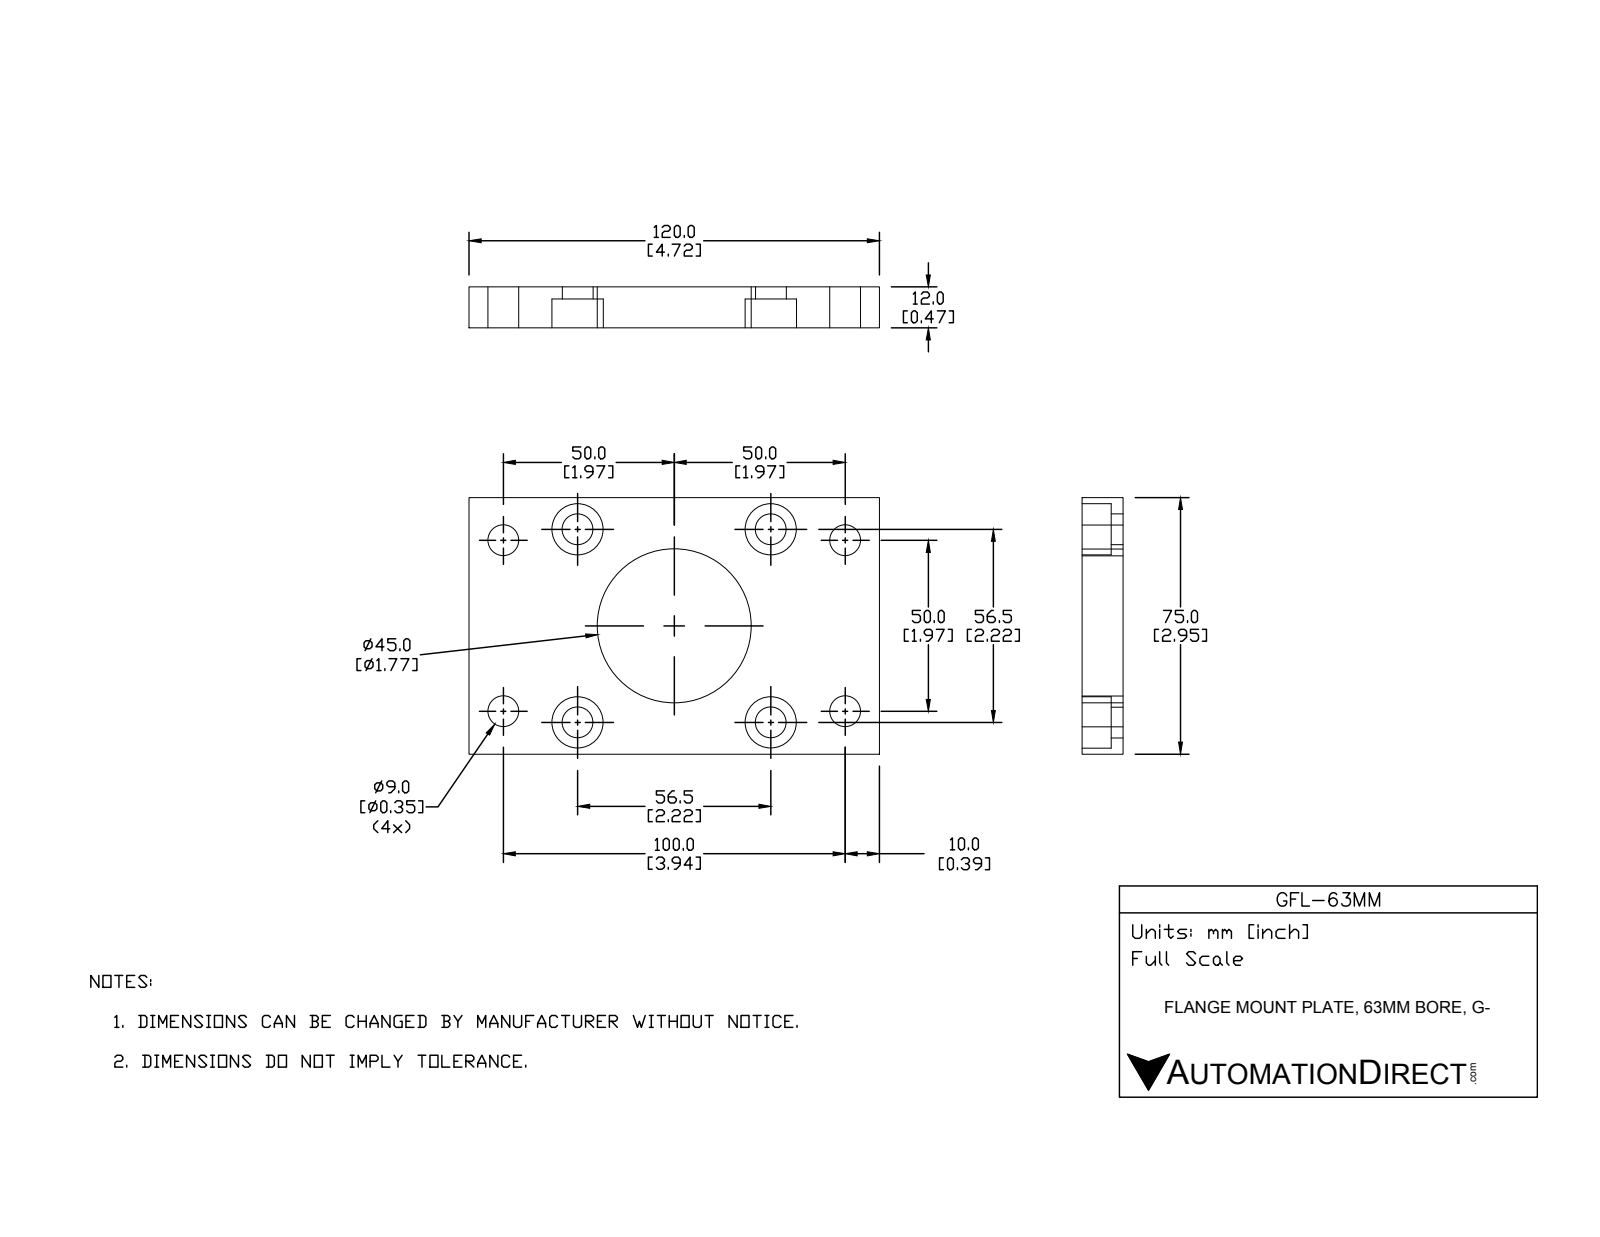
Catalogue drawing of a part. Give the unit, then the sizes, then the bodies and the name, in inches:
Units: inches
Overall size (bounding box): 4.724 × 2.953 × 0.472
Round holes (diameter × count): ⌀0.354 ×8, ⌀0.591 ×4, ⌀1.772 ×1
Main face-to-face distances: 0.472, 2.953, 4.724, 0.138, 0.335
Hole centre spacings: 0.866, 1.573, 2.201, 2.224, 2.265, 3.083, 3.726, 1.969
Volume: 4.819 in³ · Surface area: 36.48 in²
Bodies: 1 solid, 36 faces (10 planar, 26 cylindrical, 0 other)
Part name (STEP PRODUCT): GFL-63MM
STEP written by: SolidWorks 2017 (AUTOMOTIVE_DESIGN)
